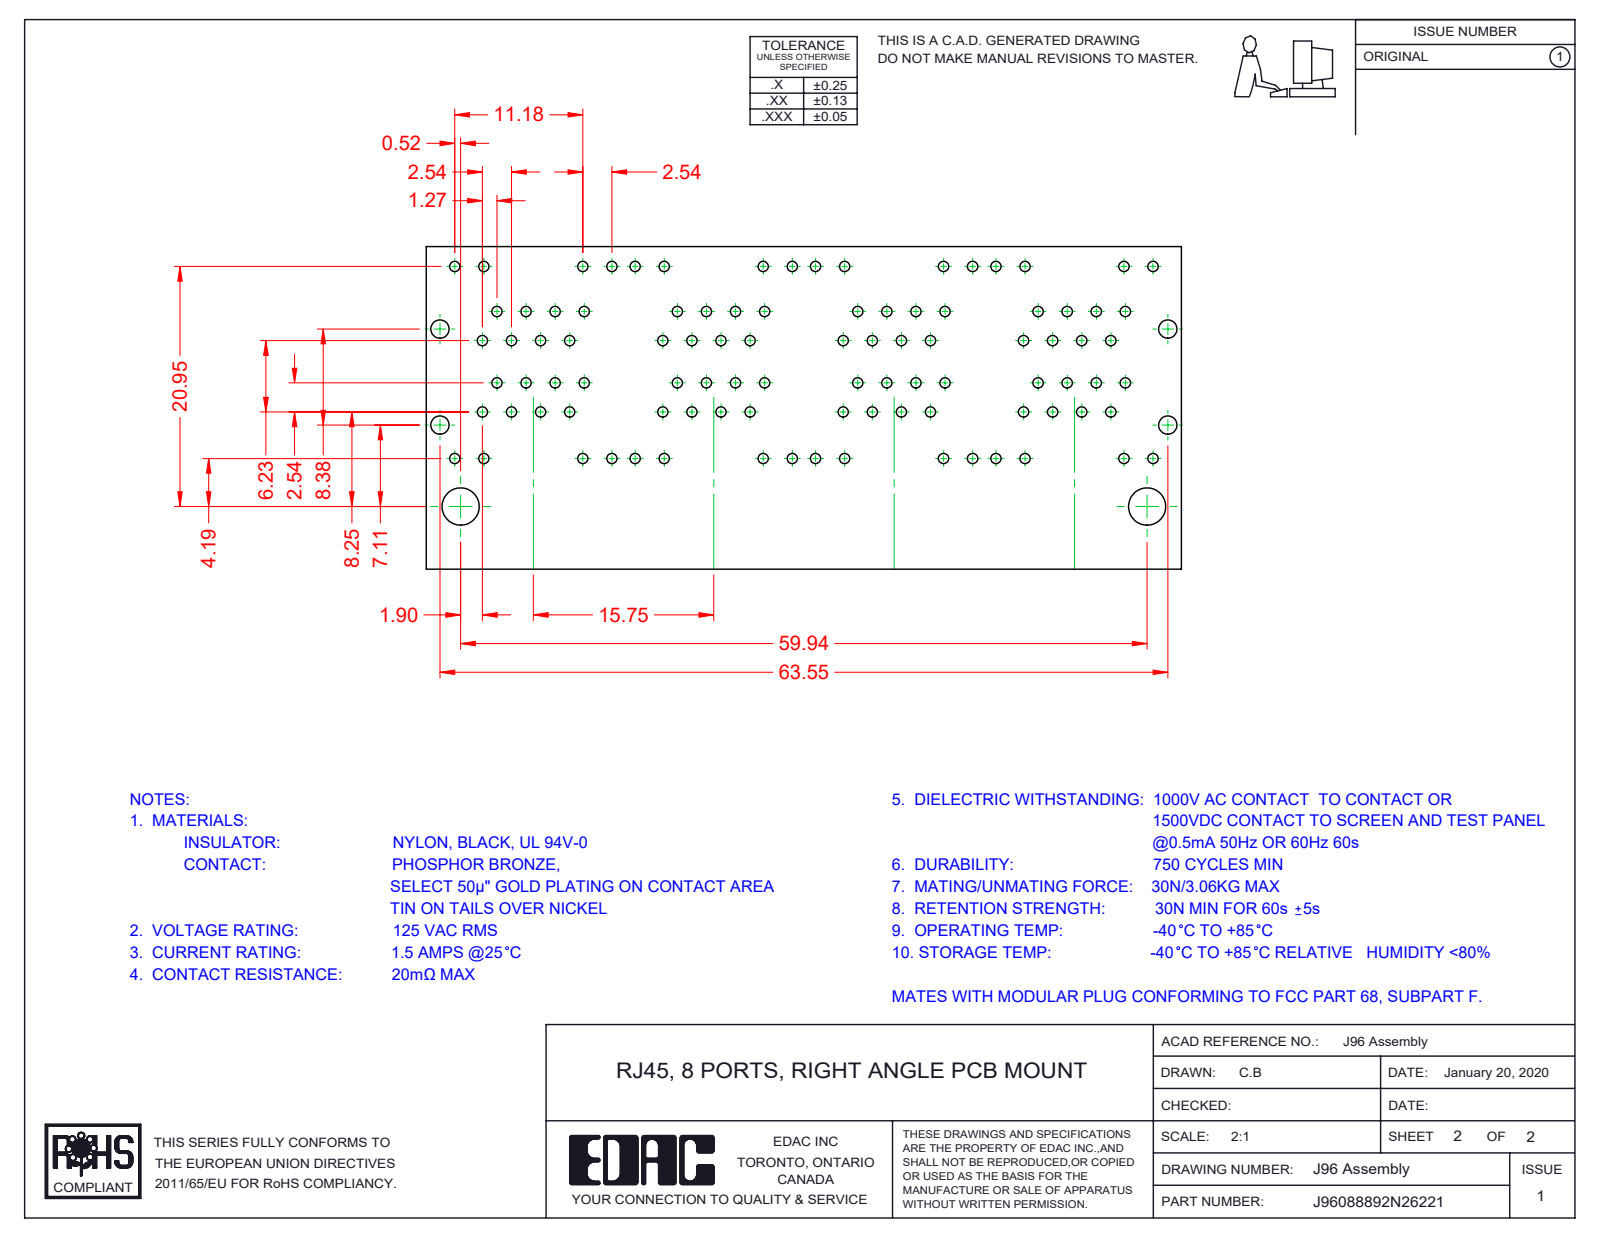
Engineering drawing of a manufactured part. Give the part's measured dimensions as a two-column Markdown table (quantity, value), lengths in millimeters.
| quantity | value |
| --- | --- |
| part name | 96 Insulator_8 Ports; 96 LED RH Lower_6-Red-Green; 96 LED LH Lower_2-Red; 96 LED LH Upper_2-Red (+8 more) |
| STEP written by | SolidWorks 2016 (CONFIG_CONTROL_DESIGN) |
| units | millimeters |
| bodies | 96 solids, 7820 faces (6105 planar, 1404 cylindrical, 311 other) |
| overall size | 67.35 × 31.38 × 28.68 |
| volume | 24 149 mm³ |
| surface area | 63 596 mm² |
| round holes (diameter × count) | 1.7 × 3 |
| round bosses / shafts (diameter × count) | 1.68 × 3 |
| partial cylindrical surfaces (radius × count) | 0.25 × 124, 0.35 × 73, 1 × 72, 0.5 × 49, 0.91 × 32, 0.2 × 27, 0.27 × 14, 0.7 × 11 |
| main face-to-face distances | 15.75, 0.35, 9.95, 1.17, 1.6, 0.54, 9.98, 10.18, 12.67, 3.37 |
| hole center spacings | 15.75, 31.5 |
